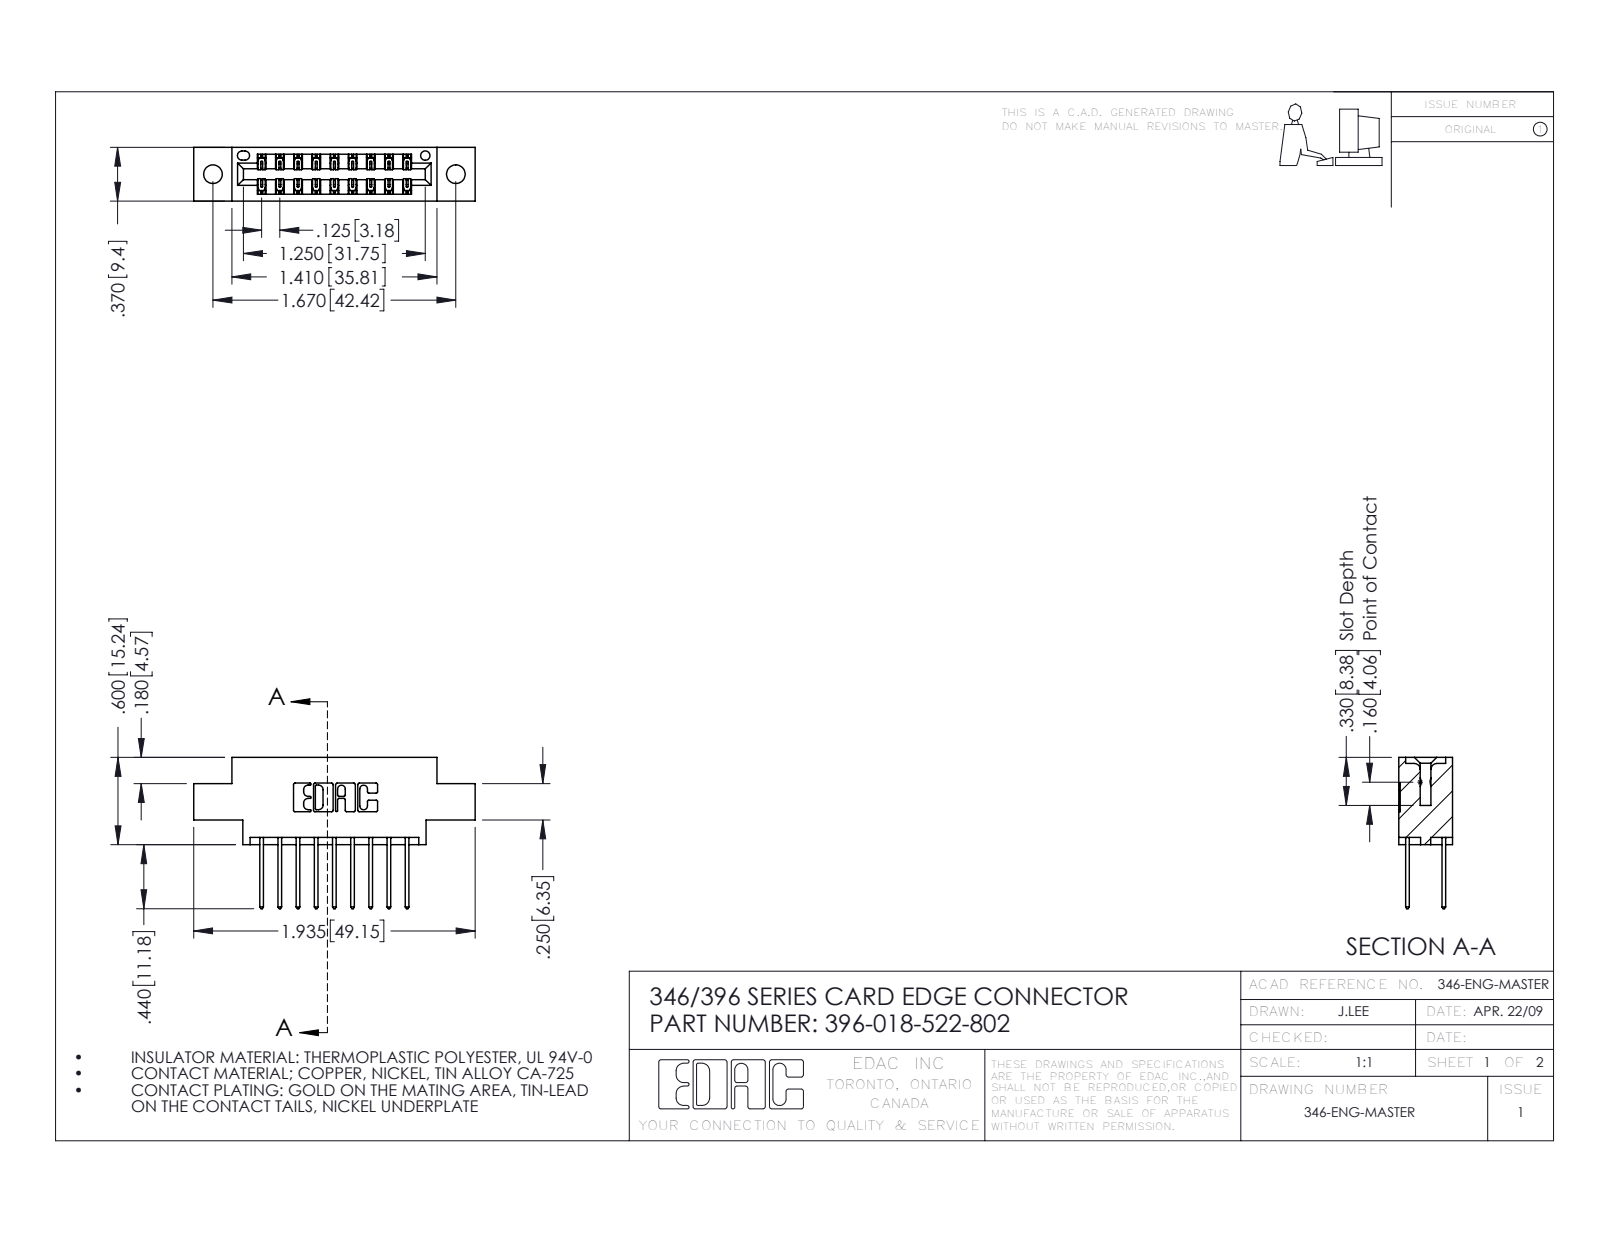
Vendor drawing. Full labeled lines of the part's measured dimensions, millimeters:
Part name (STEP PRODUCT): 345-292-001_345-293-122; 346 Part_0.170 Offset - 0.128 Dia; 396-018-522-802
STEP written by: SolidWorks 2016 (CONFIG_CONTROL_DESIGN)
Units: millimetres
Bodies: 19 solids, 1062 faces (710 planar, 352 cylindrical, 0 other)
Overall size (bounding box): 49.1 × 26.4 × 9.4
Volume: 4 390 mm³ · Surface area: 5 641 mm²
Round holes (diameter × count): ⌀3.3 ×2, ⌀1.6 ×1
Partial cylindrical surfaces — rounded edges, fillets, slot ends (radius × count): R0.2 ×27, R0.3 ×22, R0.3 ×18, R0.2 ×6, R0.8 ×6, R0.7 ×3, R0.4 ×2, R0.6 ×2
Main face-to-face distances: 6.4, 1.2, 8.2, 9.4, 1.8, 7.6, 0.6, 7, 3.8, 5.6
Hole centre spacings: 6.2, 37.2, 42.4
